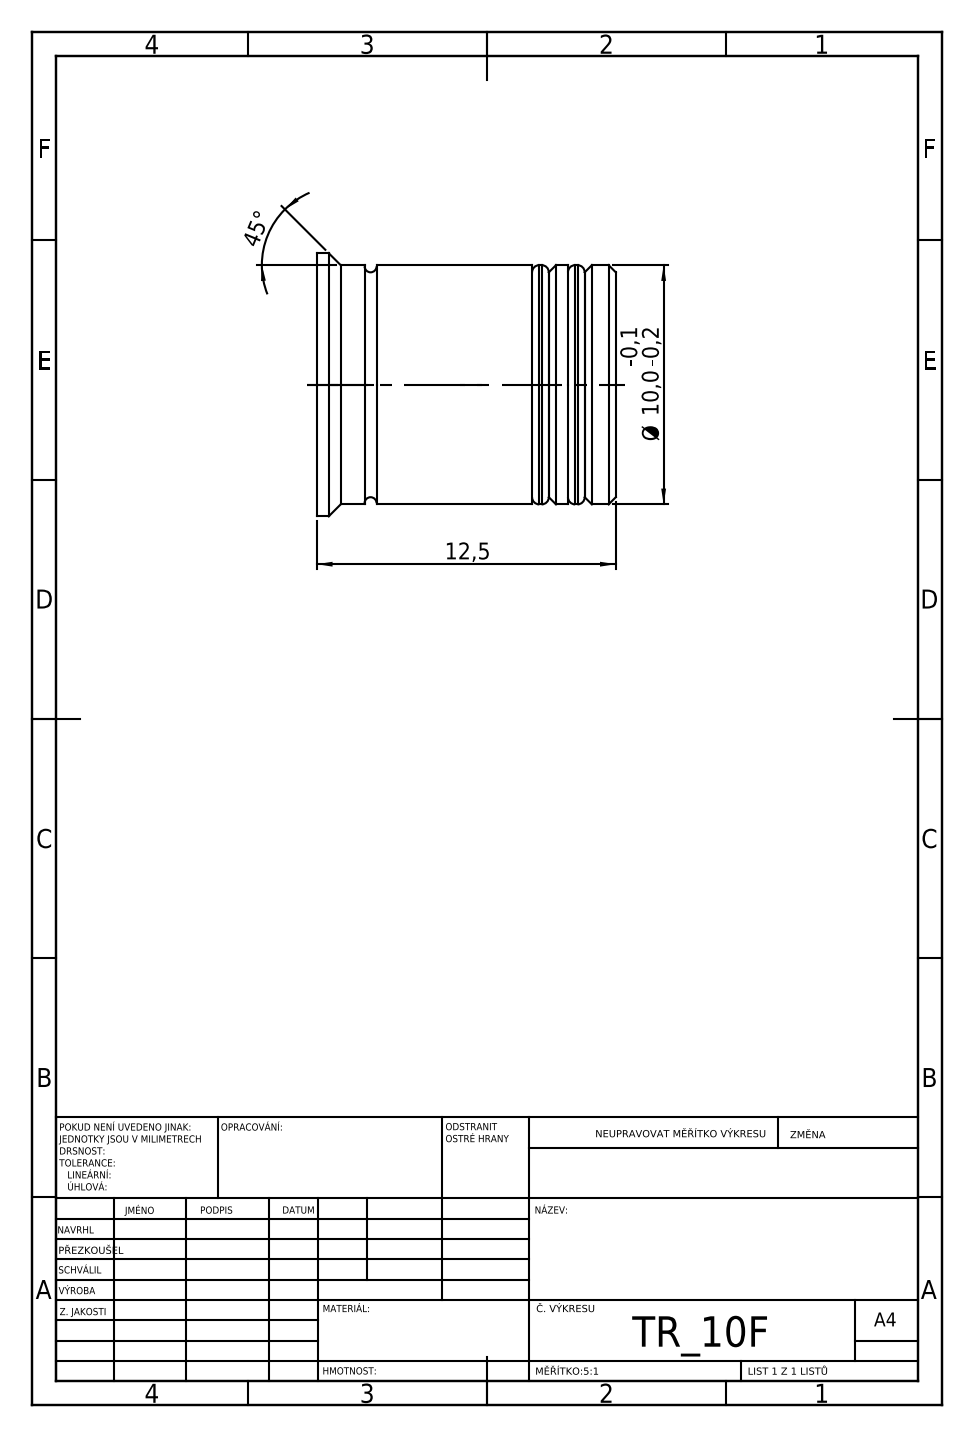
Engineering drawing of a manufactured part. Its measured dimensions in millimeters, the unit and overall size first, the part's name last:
Units: millimetres
Overall size (bounding box): 12.5 × 11 × 11
Round bosses / shafts (diameter × count): ⌀11 ×1, ⌀10 ×1, ⌀9.4 ×1, ⌀7 ×1
Main face-to-face distances: 1.5, 0.7, 2, 2.2, 0.8, 1.3, 2.8, 3.5, 8, 1
Volume: 1 032 mm³ · Surface area: 1 013 mm²
Bodies: 3 solids, 72 faces (30 planar, 20 cylindrical, 22 other)
STEP written by: SolidWorks 2019 (CONFIG_CONTROL_DESIGN)
